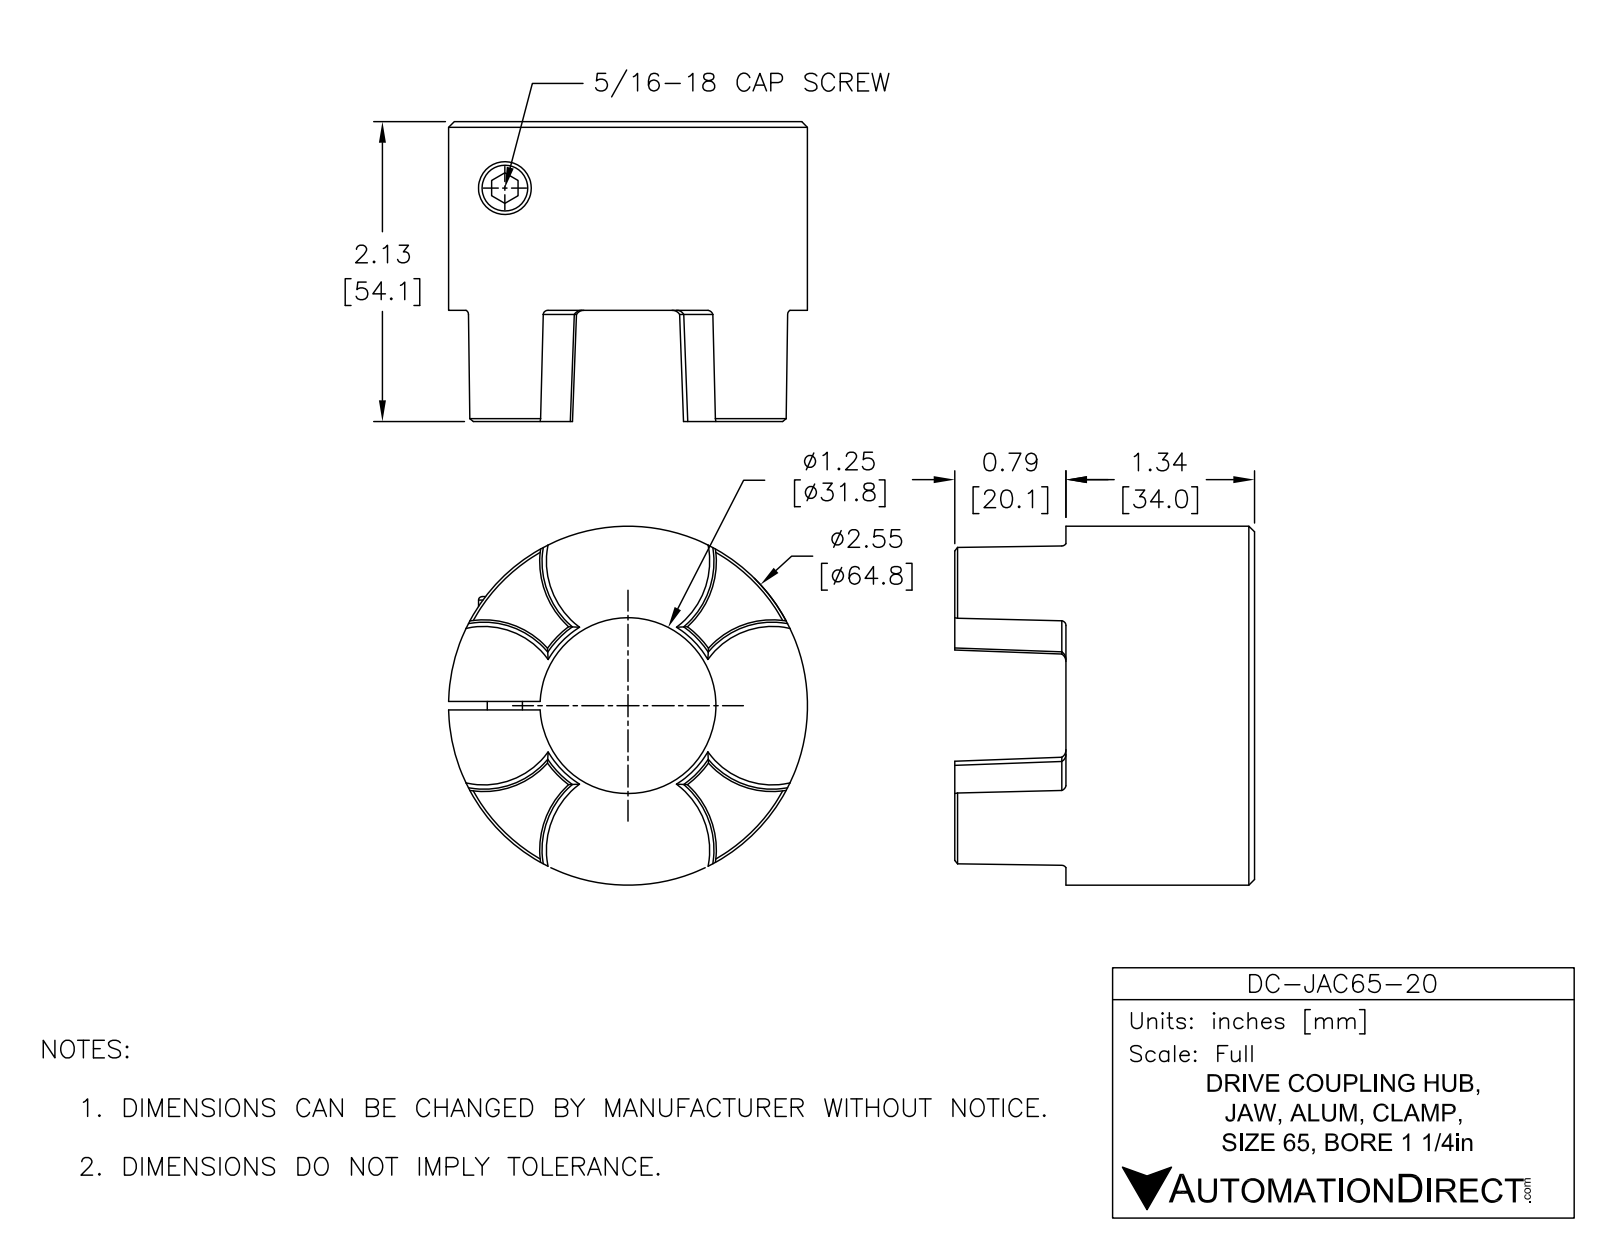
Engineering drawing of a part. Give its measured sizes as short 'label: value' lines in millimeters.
name: DC-JAC65-20
written by: SolidWorks 2015 (AUTOMOTIVE_DESIGN)
unit: mm
bodies: 1 solid, 55 faces (9 planar, 9 cylindrical, 37 other)
size: 64.77 × 64.76 × 54.1
volume: 95 024 mm³; area: 21 140 mm²
holes: 1× ⌀6.76, 1× ⌀10.31, 1× ⌀31.75
bosses: 1× ⌀64.77
face distances: 34.04, 54.1, 20.06, 1.52, 14.09, 12.57
